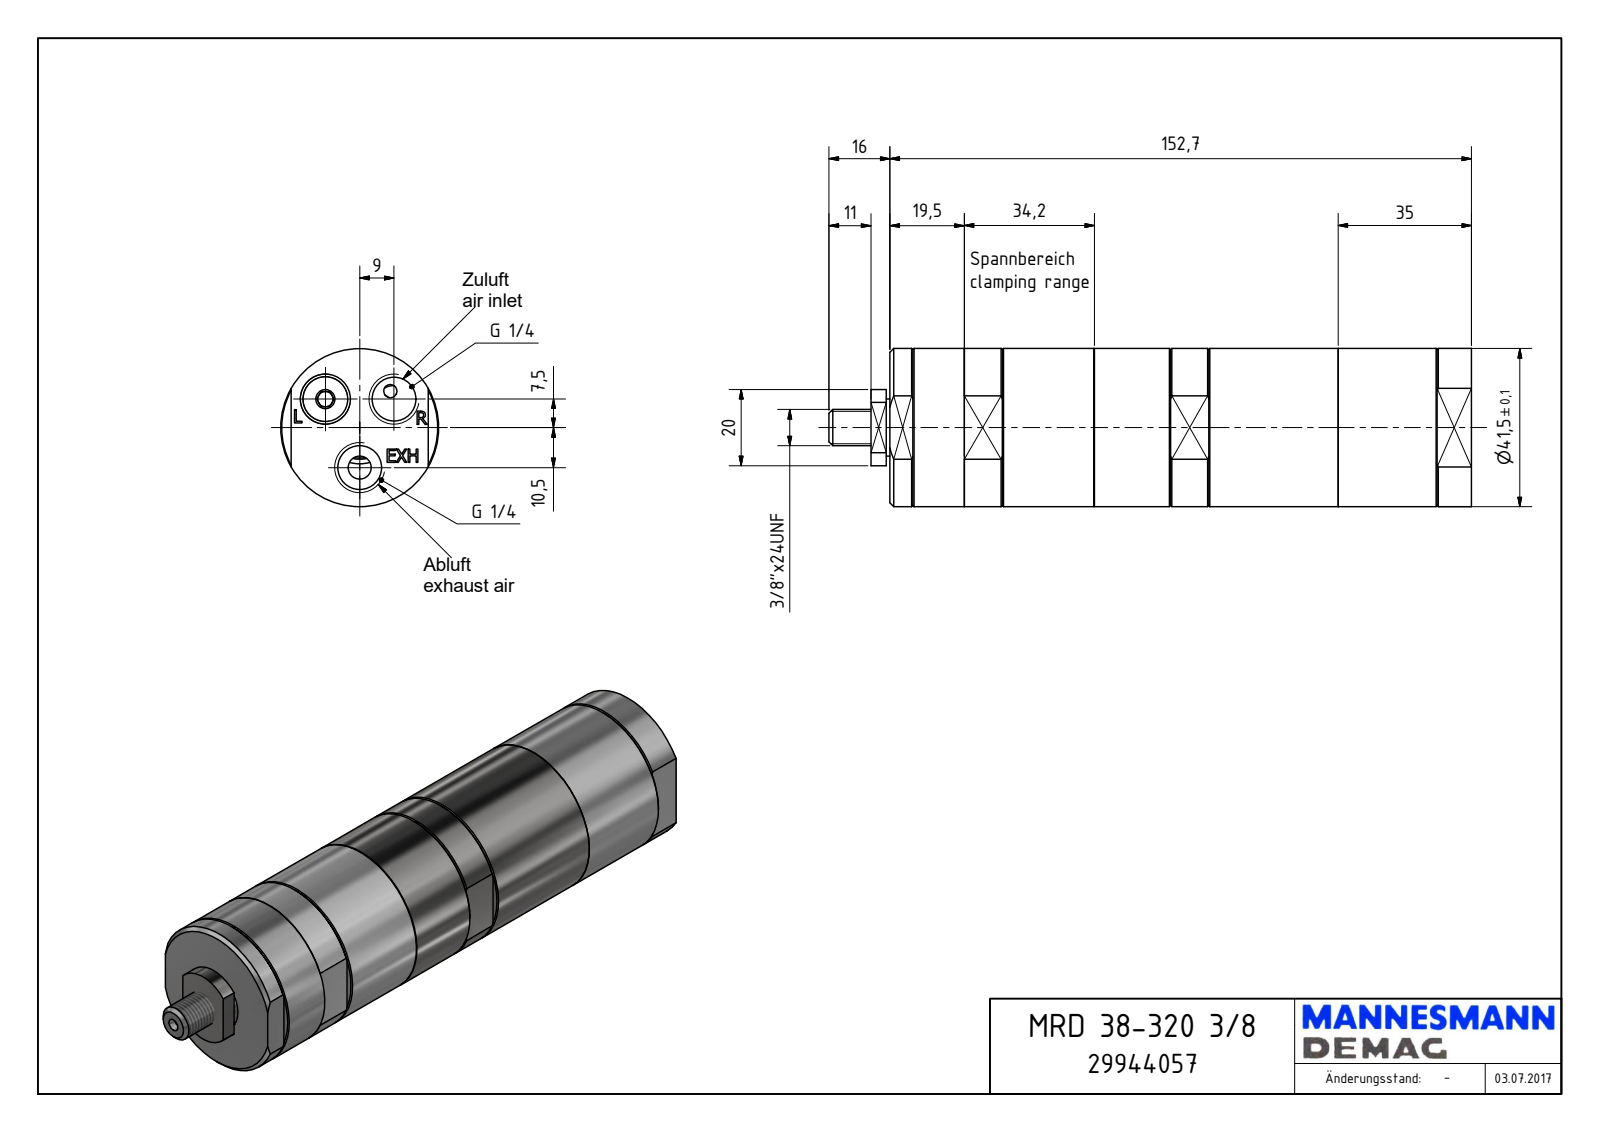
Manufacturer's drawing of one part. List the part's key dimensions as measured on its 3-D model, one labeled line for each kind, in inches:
Part name (STEP PRODUCT): MRD 38-320 3-8 D_29944057
STEP written by: Autodesk Inventor 2018 (AUTOMOTIVE_DESIGN)
Units: inches
Bodies: 1 solid, 163 faces (106 planar, 24 cylindrical, 33 other)
Overall size (bounding box): 6.642 × 1.634 × 1.634
Volume: 12.47 in³ · Surface area: 39.44 in²
Round holes (diameter × count): ⌀0.451 ×3, ⌀0.063 ×1, ⌀0.157 ×1, ⌀0.63 ×1
Round bosses / shafts (diameter × count): ⌀1.634 ×1, ⌀1.417 ×1, ⌀0.589 ×1, ⌀0.375 ×1
Partial cylindrical surfaces — rounded edges, fillets, slot ends (radius × count): R0.394 ×1
Main face-to-face distances: 6.012, 0.039, 1.496, 1.457, 2.106, 3.906, 2.114, 3.898, 5.609, 3.503
Hole centre spacings: 0.461, 0.792, 0.413, 0.709
